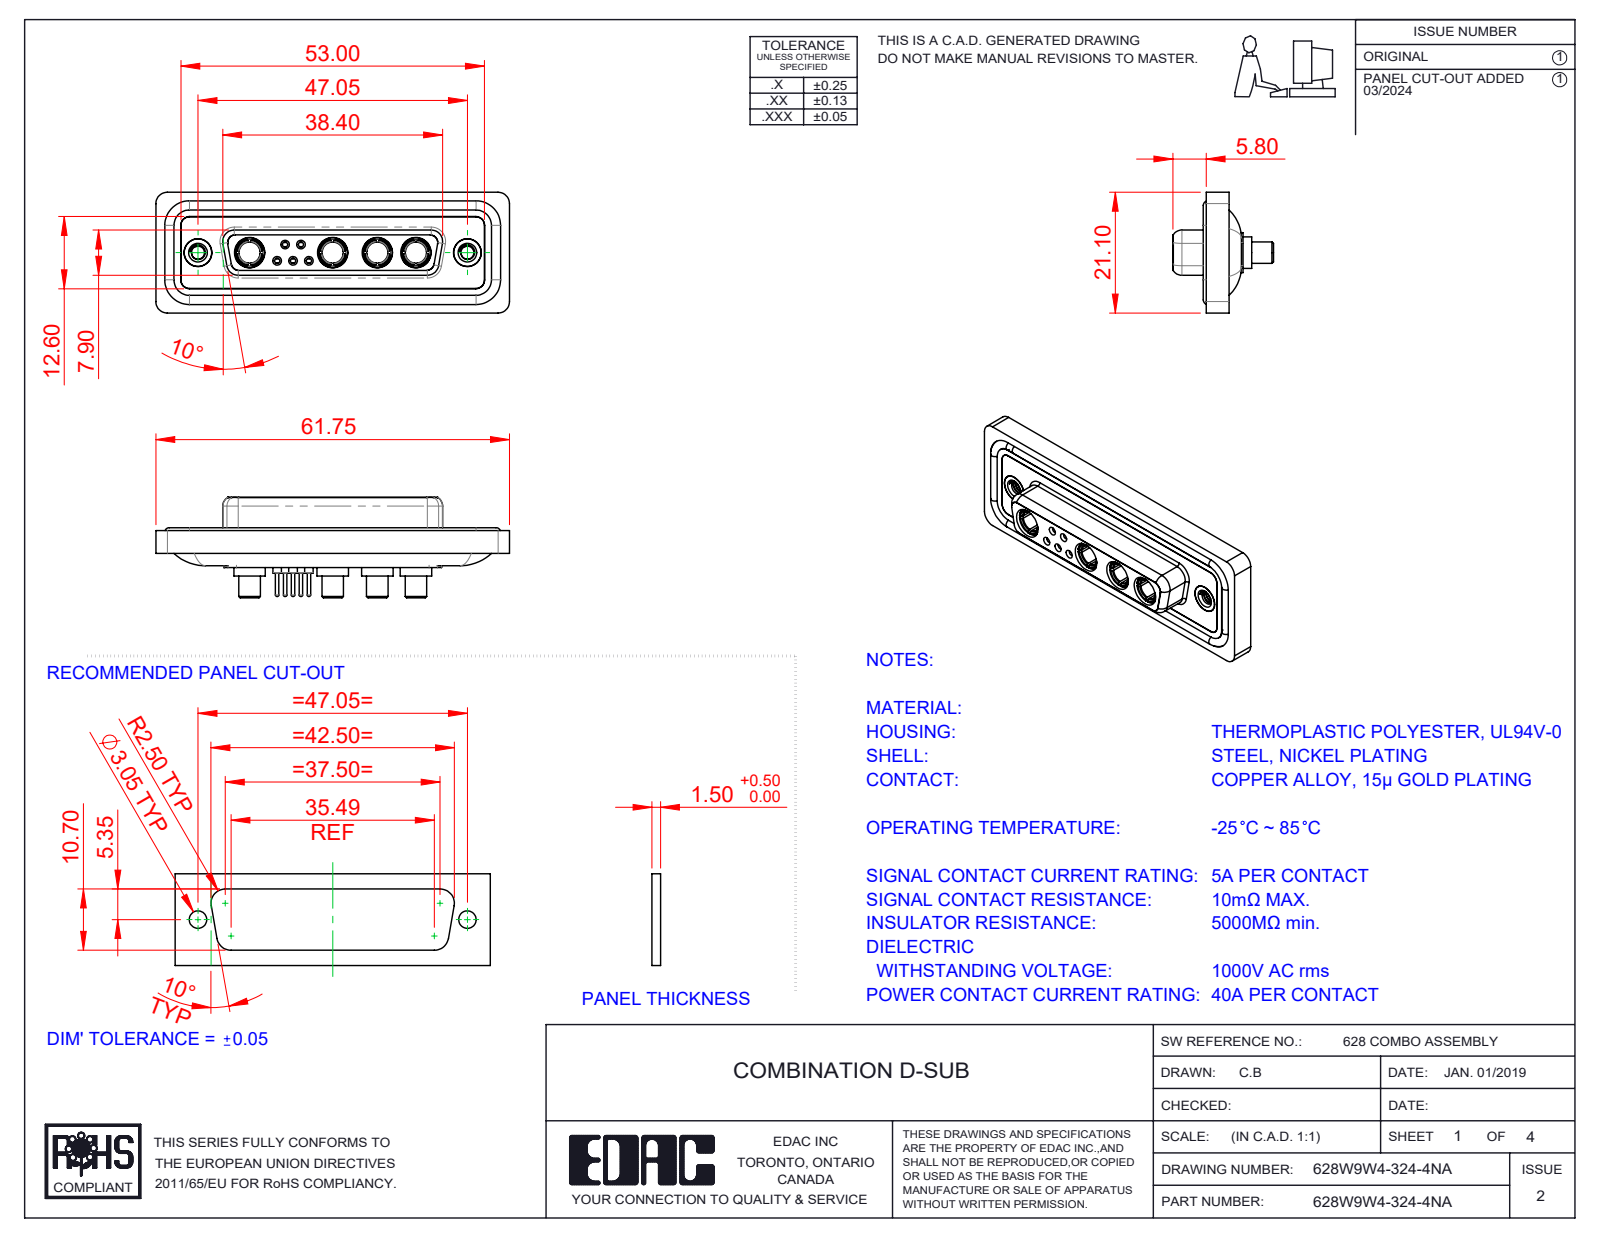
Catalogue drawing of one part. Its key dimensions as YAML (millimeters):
part_name: "628Combo Housing_9W4; 628Combo Waterproof Housing_25 Contacts; 628Combo Shell Rear_25 Contacts; 628Combo Threaded Rivet_A (+5 more)"
step_written_by: "SolidWorks 2023 (CONFIG_CONTROL_DESIGN)"
units: millimeters
bodies: {solids: 20, faces: 955, planar: 296, cylindrical: 377, other: 282}
overall_size: [61.75, 21.1, 17.55]
volume: 8299
surface_area: 13603
round_holes:
  - {diameter: 4.85, count: 6}
  - {diameter: 0.9, count: 5}
  - {diameter: 1.1, count: 5}
  - {diameter: 1.5, count: 5}
  - {diameter: 2, count: 5}
  - {diameter: 3.7, count: 4}
  - {diameter: 5.3, count: 4}
  - {diameter: 1.6, count: 3}
  - {diameter: 1.7, count: 2}
  - {diameter: 2.26, count: 2}
  - {diameter: 4, count: 2}
  - {diameter: 4.05, count: 2}
round_bosses_or_shafts:
  - {diameter: 1.6, count: 6}
  - {diameter: 2.2, count: 5}
  - {diameter: 0.6, count: 5}
  - {diameter: 5.5, count: 4}
  - {diameter: 5.2, count: 4}
  - {diameter: 4.96, count: 4}
  - {diameter: 4.75, count: 4}
  - {diameter: 3.75, count: 4}
partial_cylinders:
  - {radius: 1.5, count: 22}
  - {radius: 2, count: 18}
  - {radius: 1.35, count: 8}
  - {radius: 1.6, count: 8}
  - {radius: 0.25, count: 4}
  - {radius: 0.5, count: 4}
  - {radius: 0.6, count: 4}
  - {radius: 0.65, count: 4}
face_to_face_distances: [0.4, 1.8, 7.45, 5.65, 0.5, 7.05, 6.6, 1.6, 1.1, 2.9]
hole_center_spacings: [3.16, 2.77, 5.03, 2.76, 4.4, 5.02, 5.54, 5.73]
